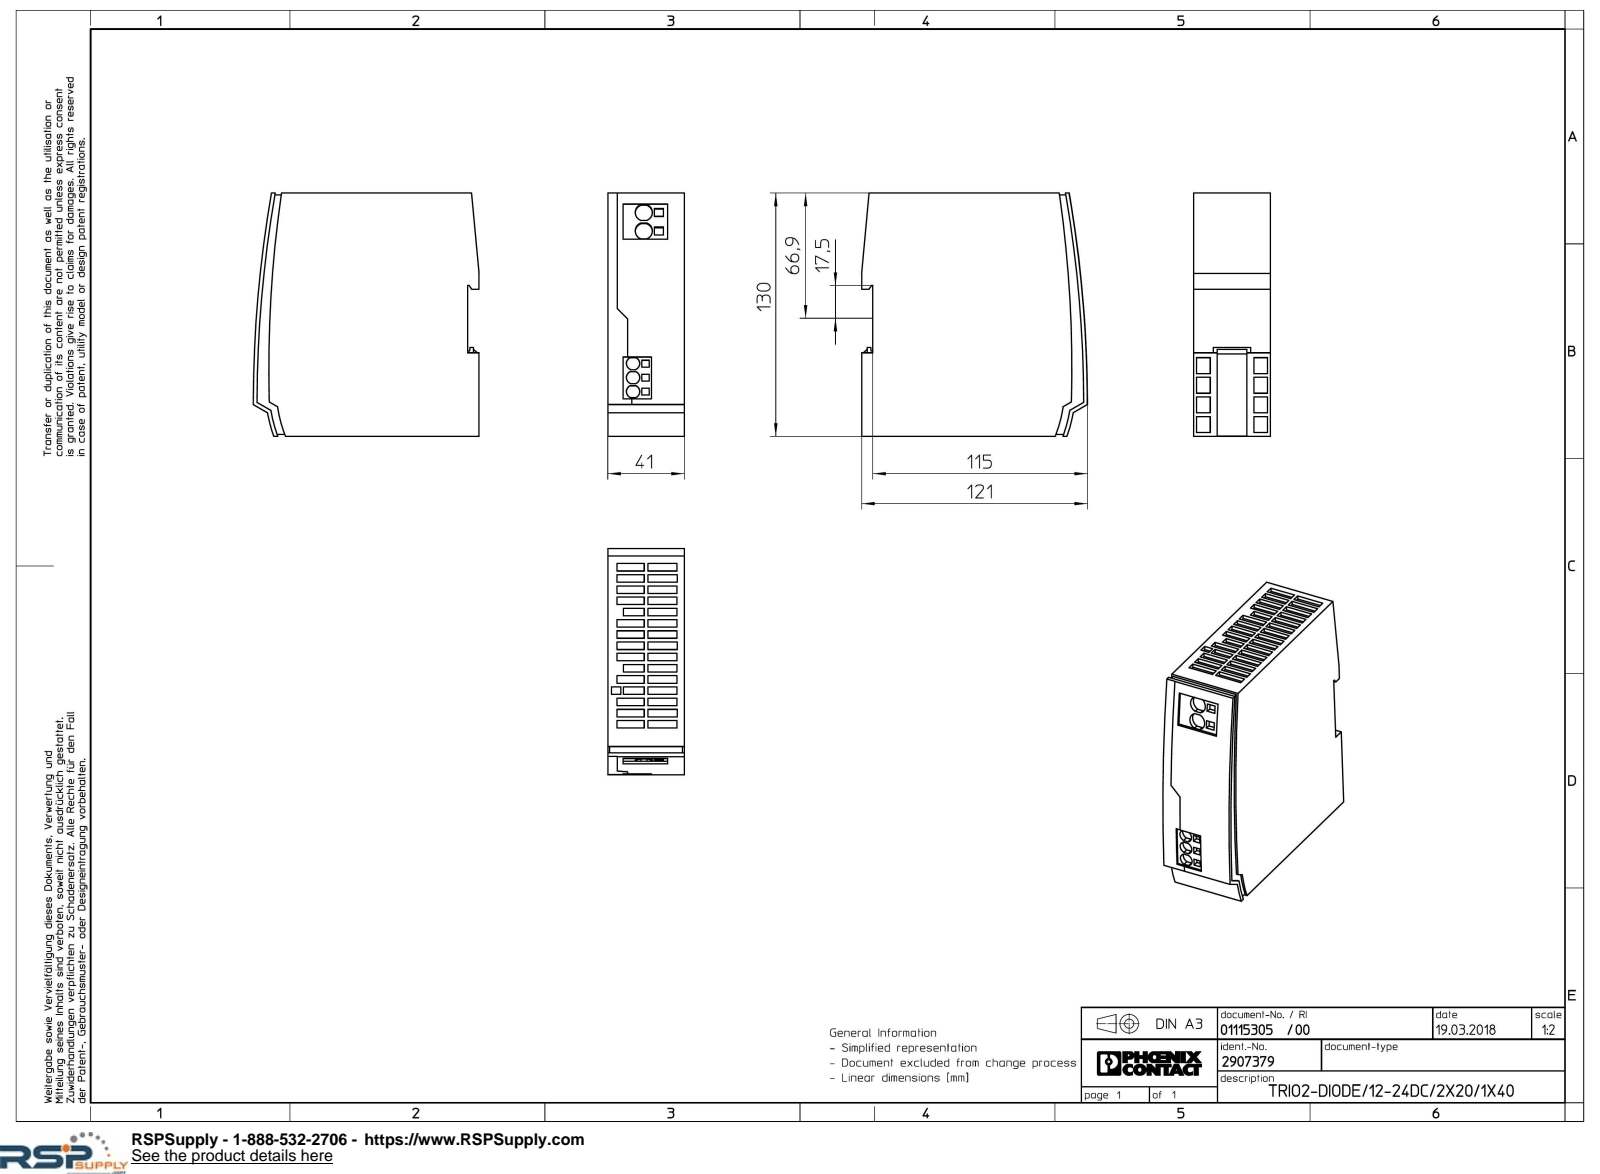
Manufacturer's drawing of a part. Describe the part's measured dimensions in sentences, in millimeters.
The part is named "TRIO2_DIODE_12_24DC_2X20_1X40-select". Its 3-D file was written by "Creo Elements/Direct Modeling 18.1I 14-Aug-2016 (C) Parametric Technology GmbH (AUTOMOTIVE_DESIGN)". It is 1 solid with 472 faces: 455 planar, 11 cylindrical and 6 other. Overall it measures 130 by 121 by 41 millimeters. Its volume is 600 526 cubic millimeters and its surface area 57 146 square millimeters. Partial cylindrical surfaces (rounded edges, fillets, slot ends): 2 of radius 4.6, 1 of radius 69.15, 1 of radius 73, 1 of radius 75, 1 of radius 655.63, 1 of radius 658, 1 of radius 659.9, 1 of radius 660. The main face-to-face distances are 41, 2, 128, 130, 6, 1, 126, 40, 4, 3.
